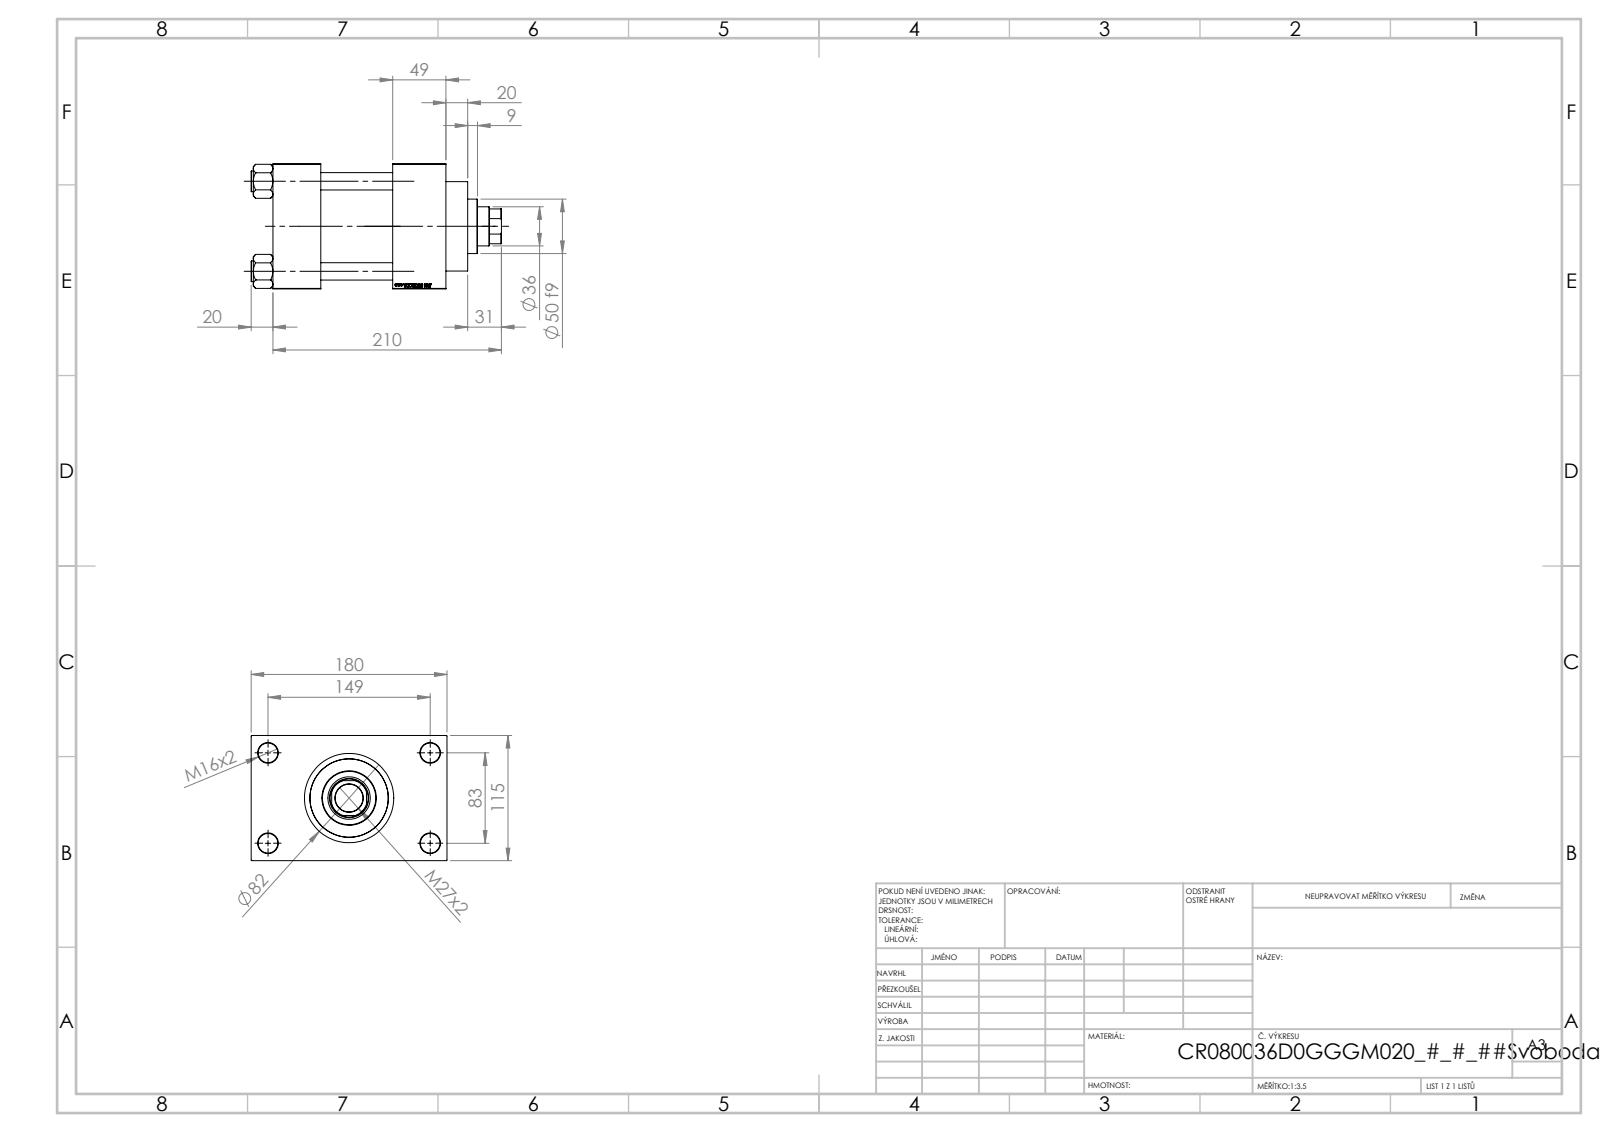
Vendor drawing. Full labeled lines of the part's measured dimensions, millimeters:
Part name (STEP PRODUCT): V215CR_D_Body; V215CR_VCP_D; V215_VC_A; V215CR_D_TYCINKA (+1 more)
STEP written by: SolidWorks 2019 (CONFIG_CONTROL_DESIGN)
Units: millimetres
Bodies: 11 solids, 1152 faces (545 planar, 89 cylindrical, 518 other)
Overall size (bounding box): 230 × 180 × 115
Volume: 1 997 000 mm³ · Surface area: 293 903 mm²
Round holes (diameter × count): ⌀16 ×4, ⌀18 ×4, ⌀7 ×2, ⌀26.44 ×2, ⌀35 ×2, ⌀25.5 ×1, ⌀36 ×1, ⌀39 ×1, ⌀61 ×1, ⌀72 ×1, ⌀80 ×1
Round bosses / shafts (diameter × count): ⌀19 ×4, ⌀86 ×1, ⌀82 ×1, ⌀50 ×1
Partial cylindrical surfaces — rounded edges, fillets, slot ends (radius × count): R17.5 ×1
Main face-to-face distances: 115, 66, 110, 49, 44, 159, 32.5, 147.5, 20, 69
Hole centre spacings: 33.15, 58.48, 82.7, 85.28, 89.24, 115.85, 142.43, 83
